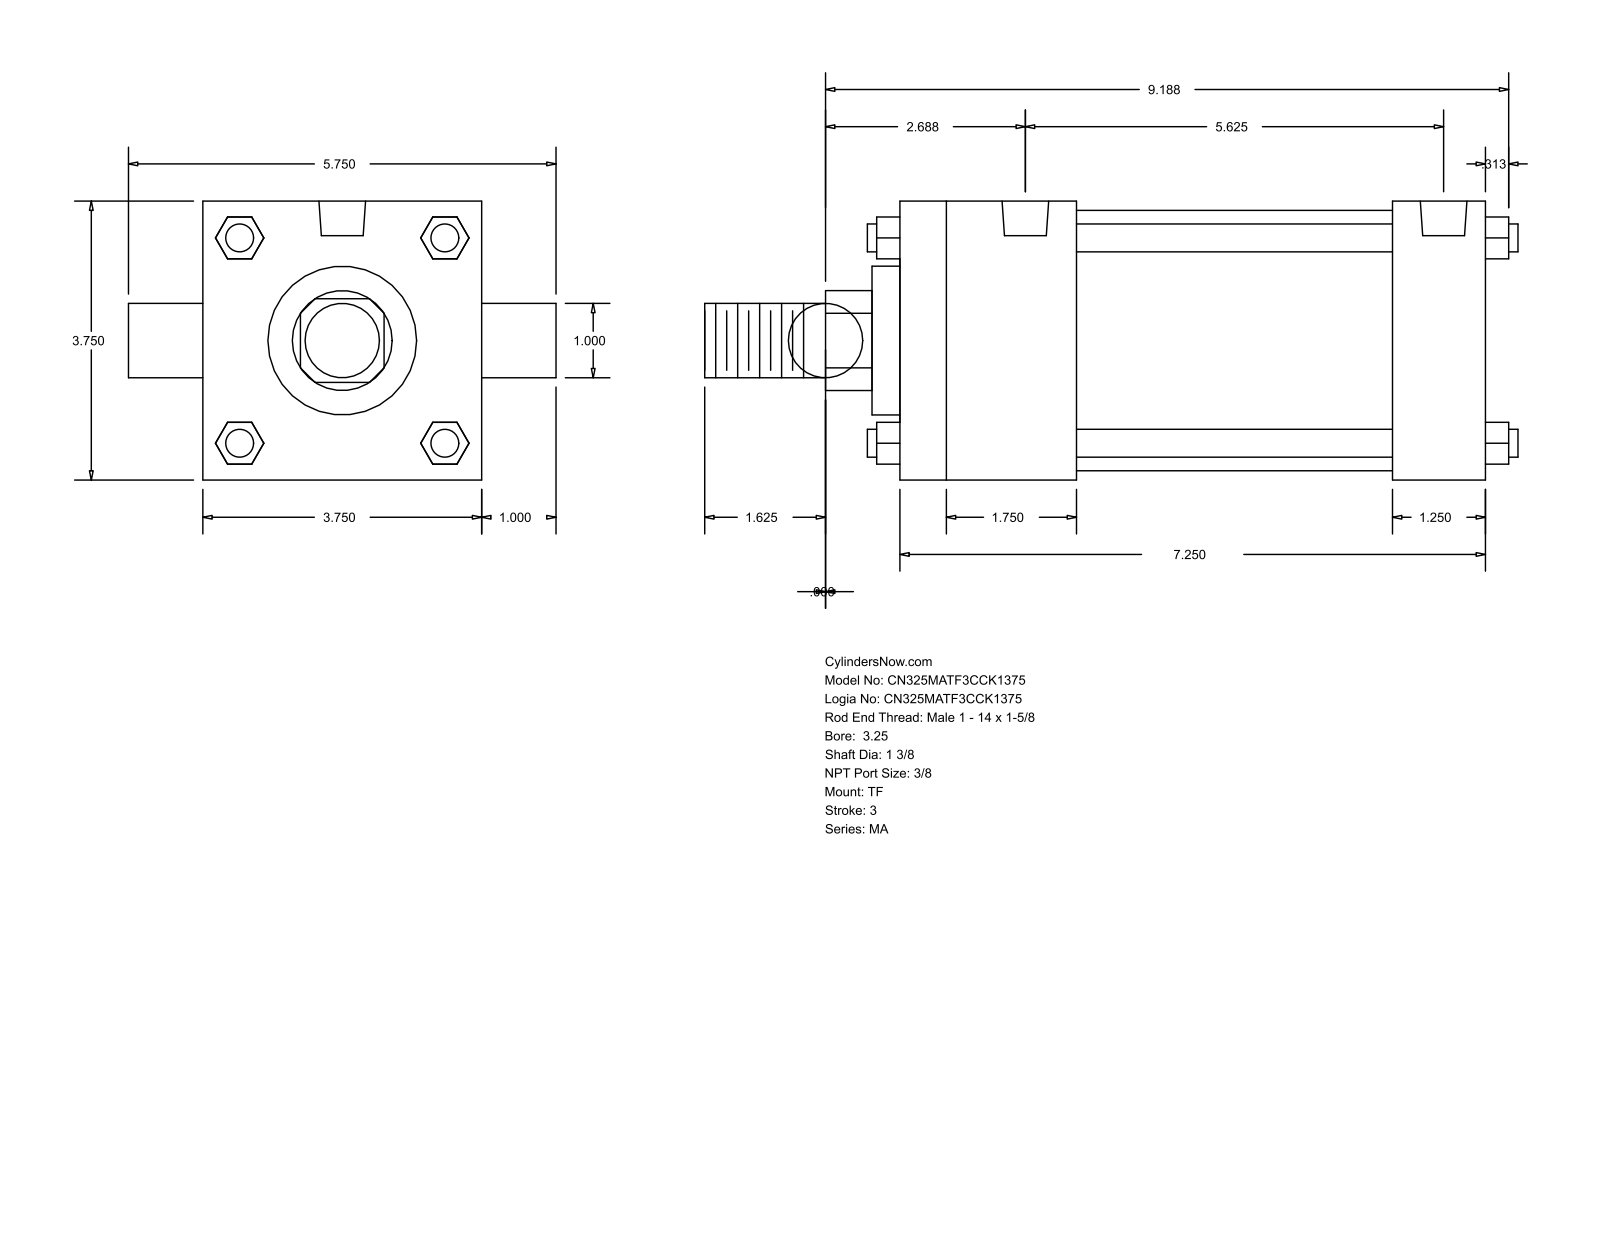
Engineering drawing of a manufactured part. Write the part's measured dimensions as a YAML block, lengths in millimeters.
part_name: "MA_TF__0325_1.375"
step_written_by: "GSSL Pune (CONFIG_CONTROL_DESIGN)"
units: millimeters
bodies: {solids: 0, faces: 120, planar: 92, cylindrical: 28, other: 0}
overall_size: [277.81, 146.05, 95.25]
round_holes:
  - {diameter: 11.11, count: 3}
  - {diameter: 15.93, count: 2}
round_bosses_or_shafts:
  - {diameter: 9.53, count: 4}
  - {diameter: 25.4, count: 2}
  - {diameter: 88.9, count: 1}
  - {diameter: 50.8, count: 1}
  - {diameter: 34.92, count: 1}
partial_cylinders:
  - {radius: 17.06, count: 1}
face_to_face_distances: [95.24, 200.03, 60.32, 168.28, 107.96, 139.71, 31.75, 9.52, 69.84, 177.8]
hole_center_spacings: [4.76, 4.77, 133.35, 138.11, 138.12, 142.88]
